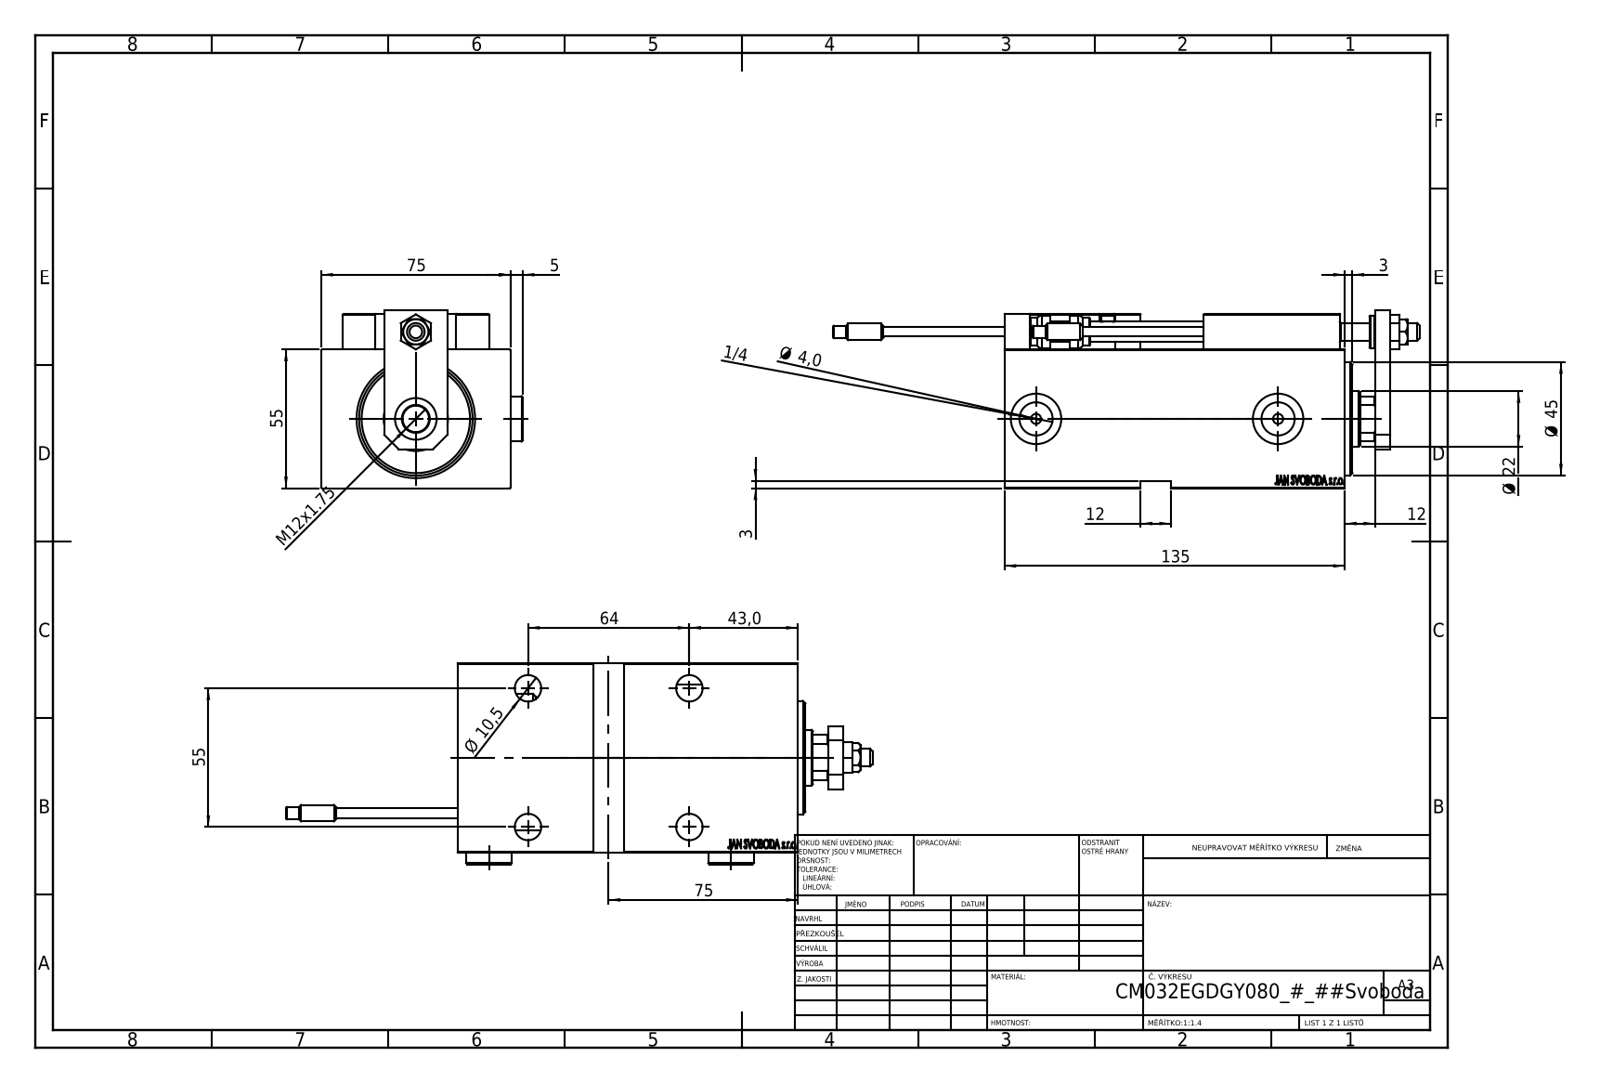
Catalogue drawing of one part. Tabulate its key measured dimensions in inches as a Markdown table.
| quantity | value |
| --- | --- |
| part name | SWITCH_X_FRONT_BACK; Zatka_OIL_PORT; SWITCH DIM B,W; ZARAZKA (+7 more) |
| STEP written by | SolidWorks 2019 (CONFIG_CONTROL_DESIGN) |
| units | inches |
| bodies | 26 solids, 1368 faces (607 planar, 204 cylindrical, 557 other) |
| overall size | 9.161 × 3.146 × 2.776 |
| volume | 33.47 in³ |
| surface area | 176.5 in² |
| round holes (diameter × count) | 0.157 × 6, 0.315 × 5, 0.413 × 5, 0.65 × 5, 0.126 × 4, 0.197 × 2, 0.518 × 2, 0.787 × 2, 0.276 × 1, 0.866 × 1, 1.004 × 1, 1.26 × 1 |
| round bosses / shafts (diameter × count) | 0.197 × 4, 0.709 × 2, 0.256 × 2, 0.15 × 2, 1.339 × 1, 0.512 × 1, 0.433 × 1 |
| partial cylindrical surfaces (radius × count) | 0.012 × 30, 0.118 × 2, 0.413 × 1 |
| main face-to-face distances | 2.165, 2.953, 0.394, 2.717, 0.118, 0.551, 0.472, 5.315, 0.197, 0.984 |
| hole center spacings | 0.448, 0.787, 1.138, 1.165, 1.169, 1.42, 1.576, 1.661 |
